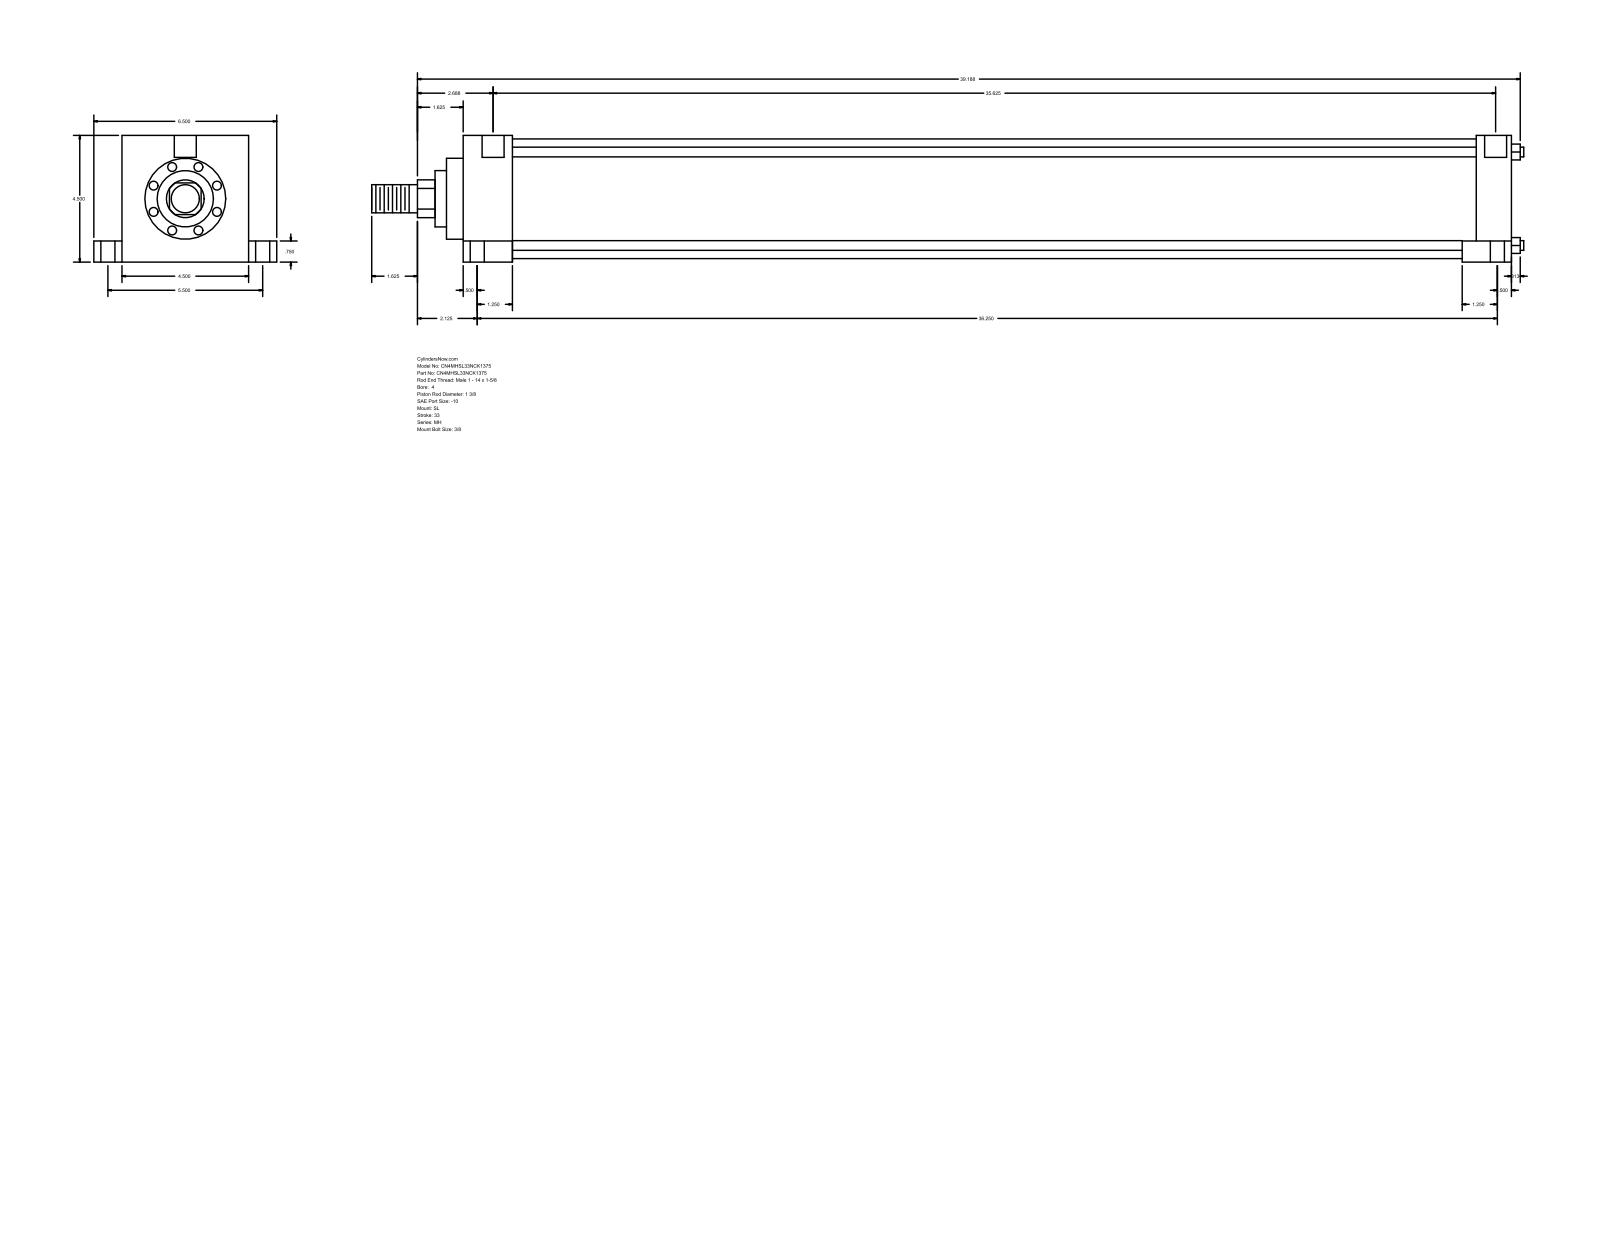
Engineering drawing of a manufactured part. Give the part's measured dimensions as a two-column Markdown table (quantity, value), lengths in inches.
| quantity | value |
| --- | --- |
| part name | MH_SL__0400_1.375 |
| STEP written by | GSSL Pune (CONFIG_CONTROL_DESIGN) |
| units | inches |
| bodies | 0 solids, 110 faces (77 planar, 33 cylindrical, 0 other) |
| overall size | 40.937 × 6.5 × 4.5 |
| round holes (diameter × count) | 0.344 × 4, 0.5 × 4, 0.75 × 4, 0.781 × 2 |
| round bosses / shafts (diameter × count) | 0.345 × 4, 4.25 × 1, 2.875 × 1, 2 × 1, 1.375 × 1, 1 × 1 |
| partial cylindrical surfaces (radius × count) | 0.672 × 1 |
| main face-to-face distances | 4.5, 37.25, 1.75, 35.5, 36, 34.25, 1.25, 1, 5.5, 0.75 |
| hole center spacings | 0.063, 2.75, 2.751, 2.795, 2.807, 5.5, 35.688, 35.75 |
